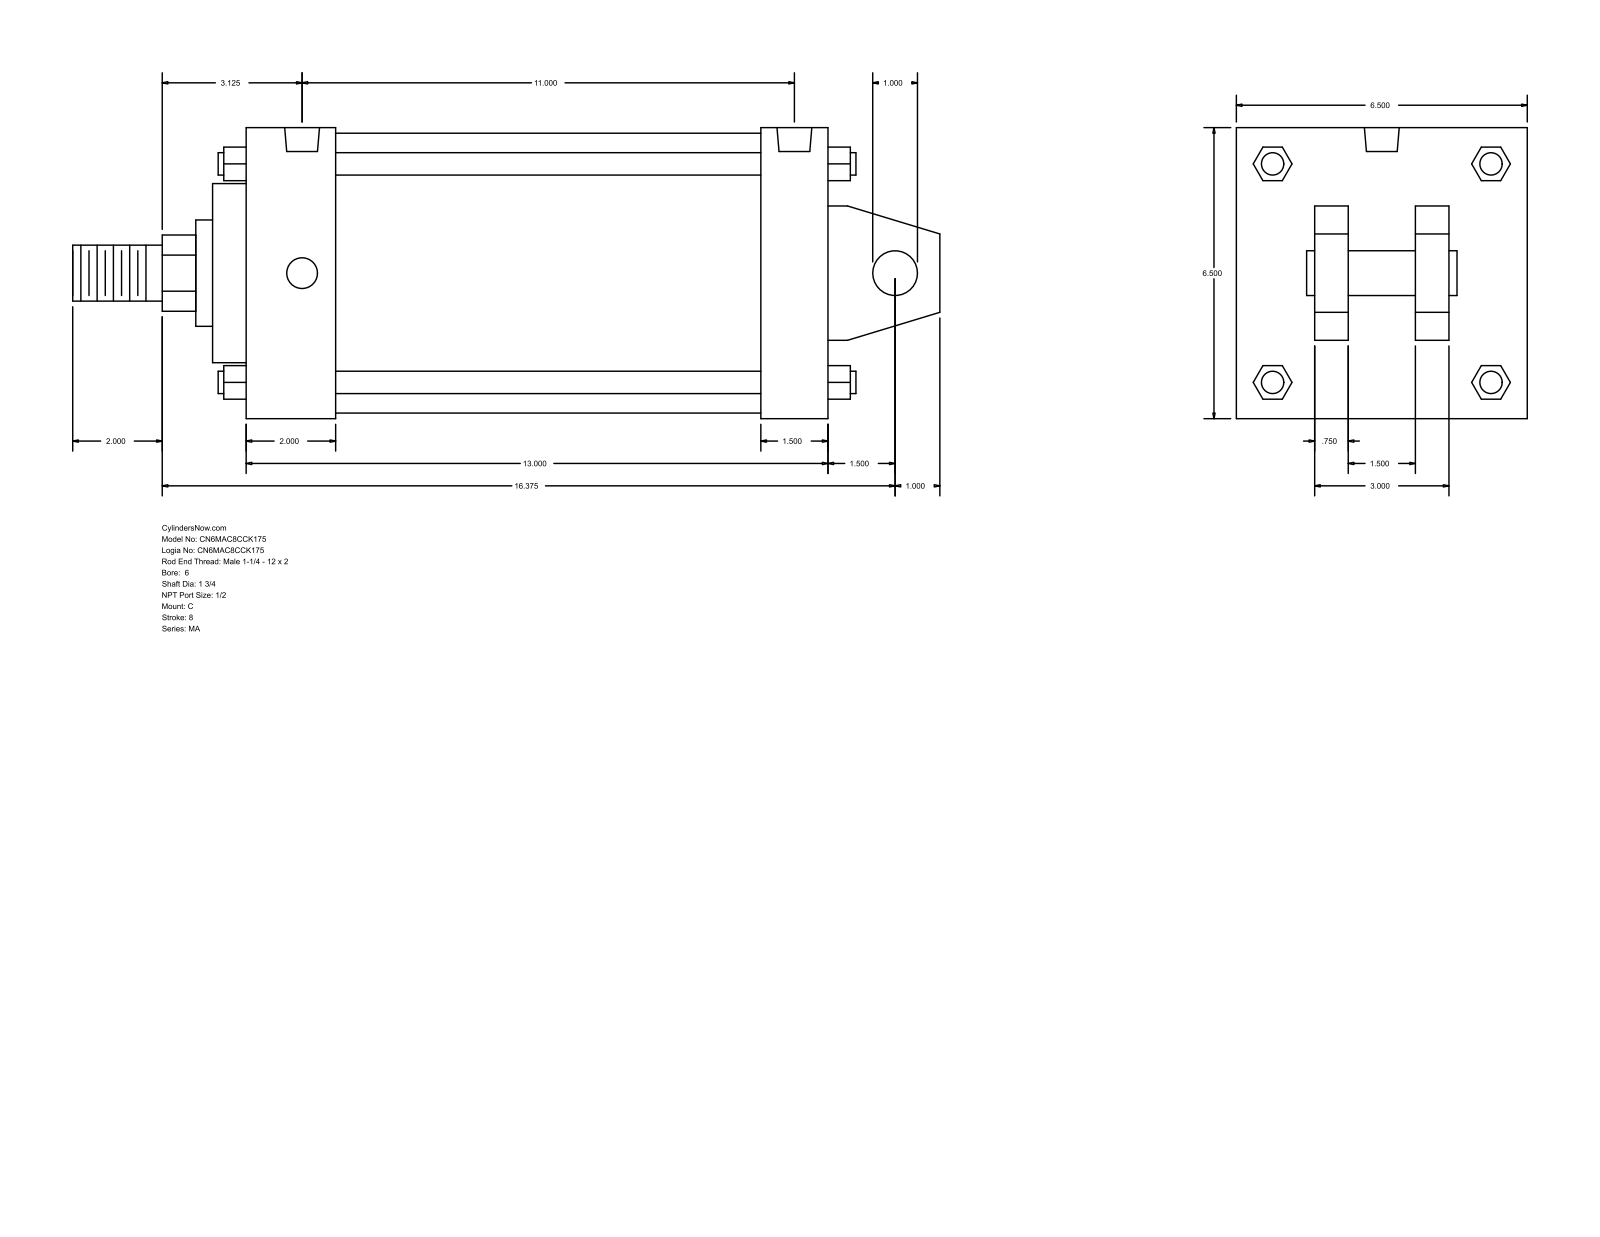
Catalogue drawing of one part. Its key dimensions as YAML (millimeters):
part_name: "MA_C__0600_1.75"
step_written_by: "GSSL Pune (CONFIG_CONTROL_DESIGN)"
units: millimeters
bodies: {solids: 0, faces: 141, planar: 109, cylindrical: 32, other: 0}
overall_size: [492.12, 165.1, 165.1]
round_holes:
  - {diameter: 17.46, count: 4}
  - {diameter: 19.77, count: 2}
round_bosses_or_shafts:
  - {diameter: 12.7, count: 4}
  - {diameter: 158.75, count: 1}
  - {diameter: 101.6, count: 1}
  - {diameter: 60.33, count: 1}
  - {diameter: 44.45, count: 1}
  - {diameter: 31.75, count: 1}
  - {diameter: 25.4, count: 1}
partial_cylinders:
  - {radius: 21.63, count: 1}
face_to_face_distances: [165.1, 330.2, 19.05, 63.5, 101.6, 50.8, 120.65, 44.45, 57.15, 279.4]
hole_center_spacings: [279.39]
